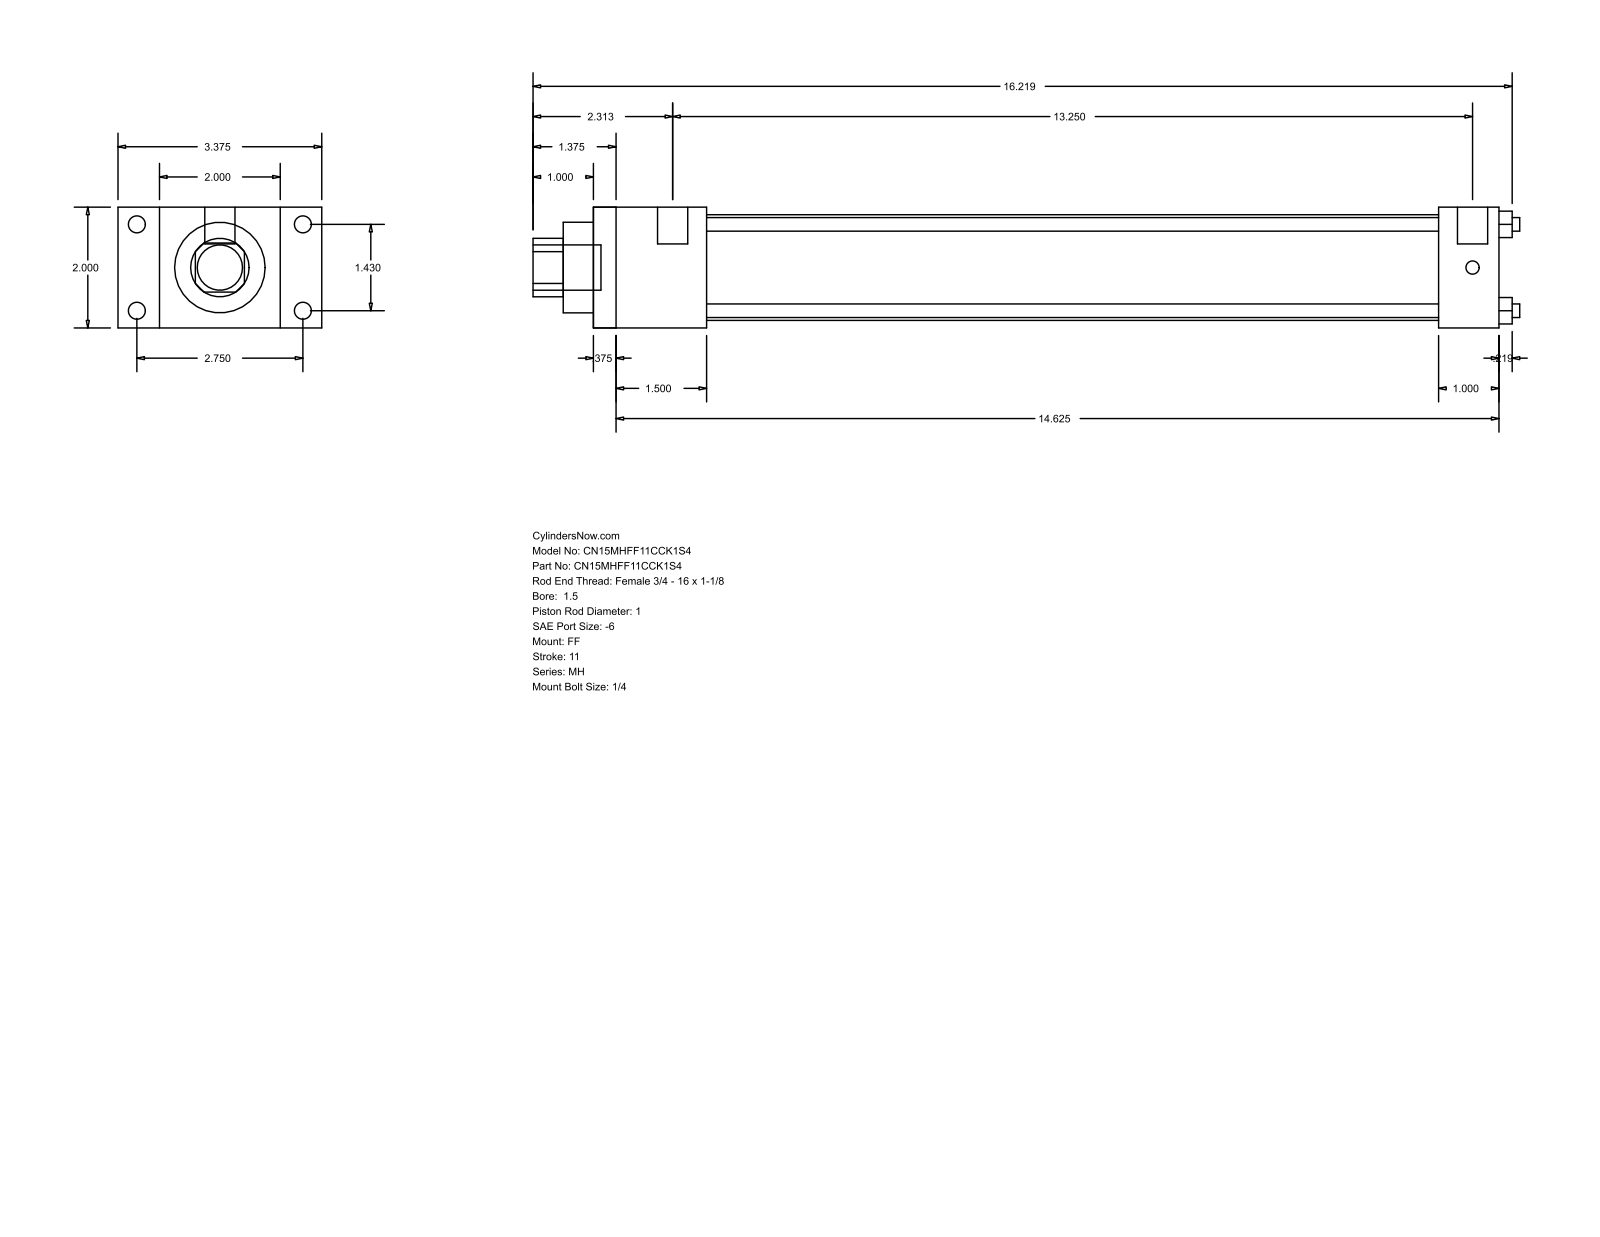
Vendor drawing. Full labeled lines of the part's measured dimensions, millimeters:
Part name (STEP PRODUCT): MH_FF__0150_1
STEP written by: GSSL Pune (CONFIG_CONTROL_DESIGN)
Units: millimetres
Bodies: 0 solids, 92 faces (64 planar, 28 cylindrical, 0 other)
Overall size (bounding box): 415.13 × 85.72 × 50.8
Round holes (diameter × count): ⌀5.71 ×4, ⌀25.4 ×1, ⌀38.1 ×1, ⌀44.45 ×1
Round bosses / shafts (diameter × count): ⌀7.14 ×4, ⌀5.56 ×4, ⌀12.7 ×2, ⌀19.05 ×1
Partial cylindrical surfaces — rounded edges, fillets, slot ends (radius × count): R12.29 ×1
Main face-to-face distances: 50.8, 381, 9.52, 371.48, 25.4, 17.46, 68.26, 47.63, 38.11, 333.37
Hole centre spacings: 25.68, 36.32, 51.36
